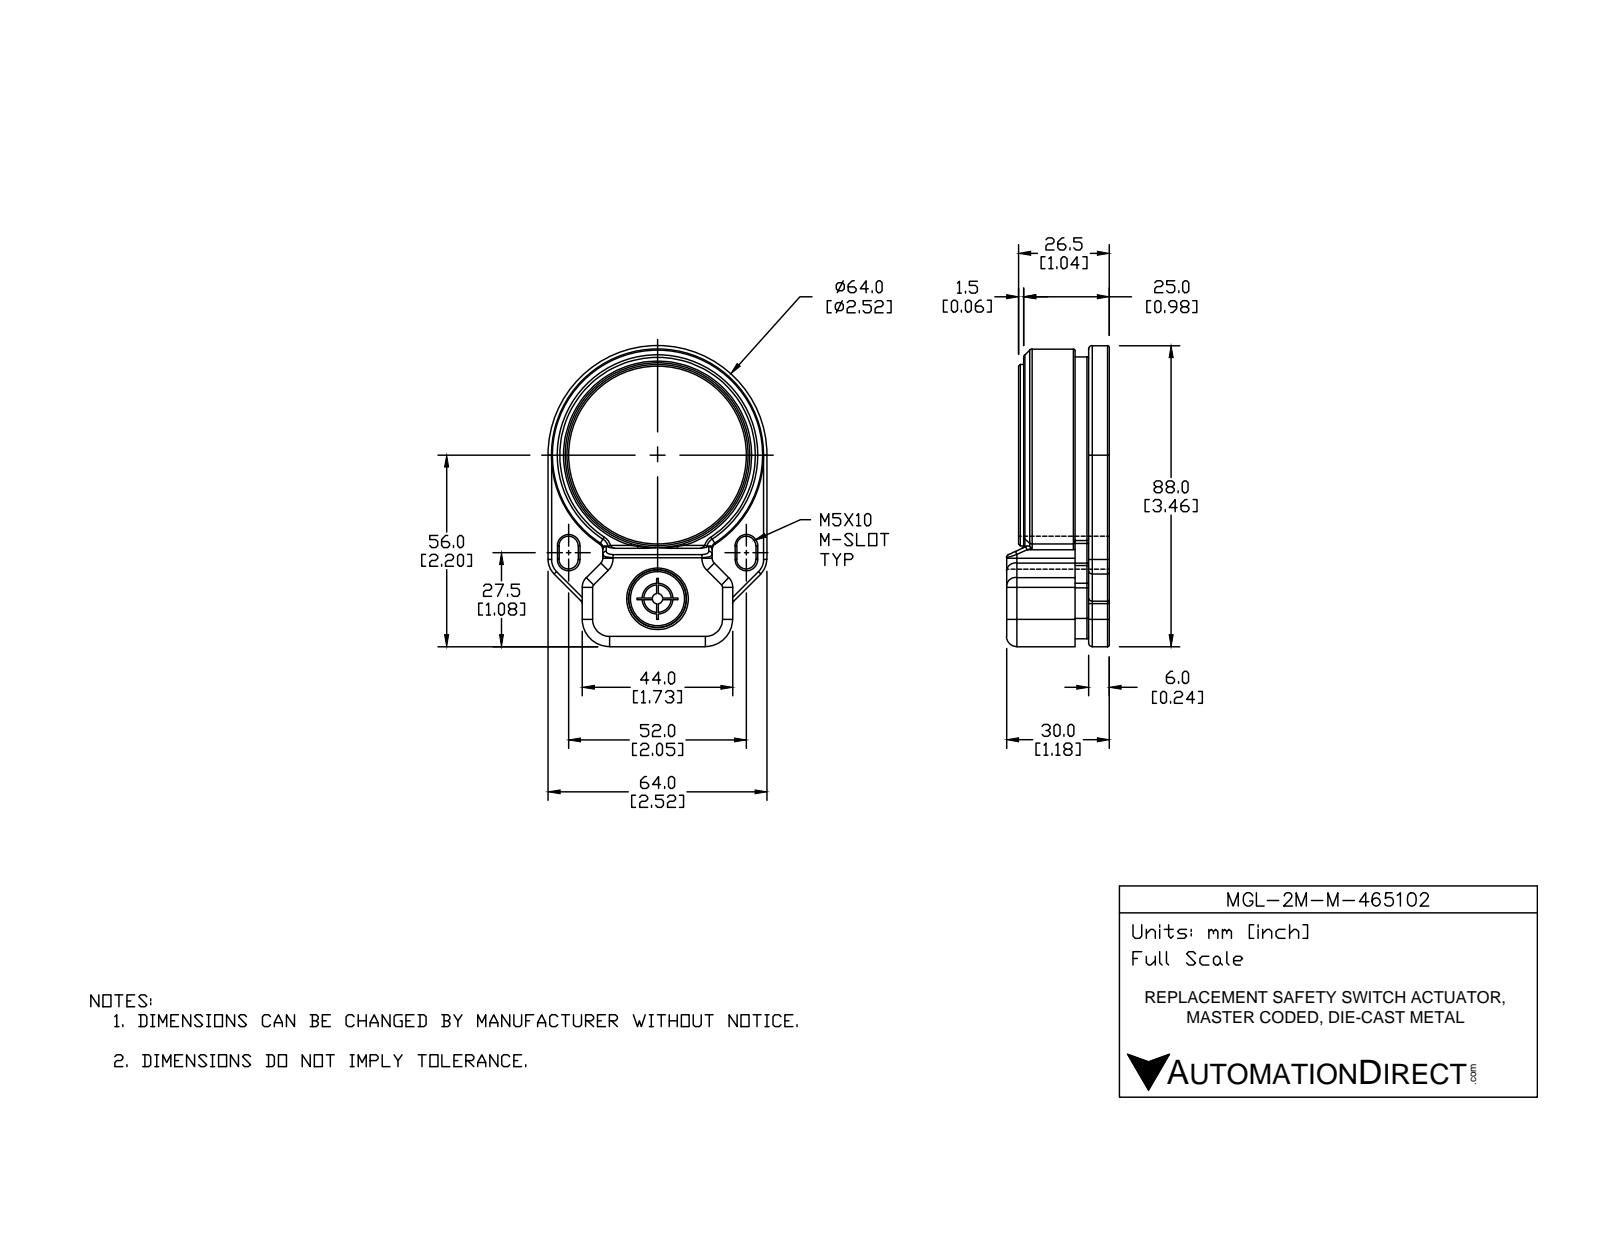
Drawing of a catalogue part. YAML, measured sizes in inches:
part_name: "MGL-2M-M-465102"
step_written_by: "SolidWorks 2017 (AUTOMOTIVE_DESIGN)"
units: inches
bodies: {solids: 7, faces: 768, planar: 158, cylindrical: 319, other: 291}
overall_size: [3.465, 2.52, 1.181]
volume: 5.043
surface_area: 78.37
round_holes:
  - {diameter: 0.315, count: 6}
  - {diameter: 0.323, count: 3}
  - {diameter: 0.098, count: 2}
  - {diameter: 0.13, count: 2}
  - {diameter: 0.157, count: 2}
  - {diameter: 0.197, count: 2}
  - {diameter: 0.669, count: 2}
  - {diameter: 0.276, count: 1}
  - {diameter: 0.354, count: 1}
  - {diameter: 0.374, count: 1}
  - {diameter: 0.394, count: 1}
  - {diameter: 0.413, count: 1}
round_bosses_or_shafts:
  - {diameter: 2.441, count: 1}
  - {diameter: 2.26, count: 1}
  - {diameter: 2.087, count: 1}
  - {diameter: 0.906, count: 1}
  - {diameter: 0.661, count: 1}
  - {diameter: 0.551, count: 1}
  - {diameter: 0.512, count: 1}
  - {diameter: 0.402, count: 1}
partial_cylinders:
  - {radius: 0.02, count: 92}
  - {radius: 0.039, count: 36}
  - {radius: 0.079, count: 24}
  - {radius: 0.118, count: 9}
  - {radius: 0.024, count: 7}
  - {radius: 0.236, count: 6}
  - {radius: 0.11, count: 4}
  - {radius: 0.157, count: 3}
face_to_face_distances: [0.413, 0.65, 0.236, 0.098, 0.492, 0.394, 0.059, 0.295, 0.256, 0.315]
hole_center_spacings: [0.768, 1.086, 0.376, 0.548, 0.579, 0.898, 1.127, 1.198]
